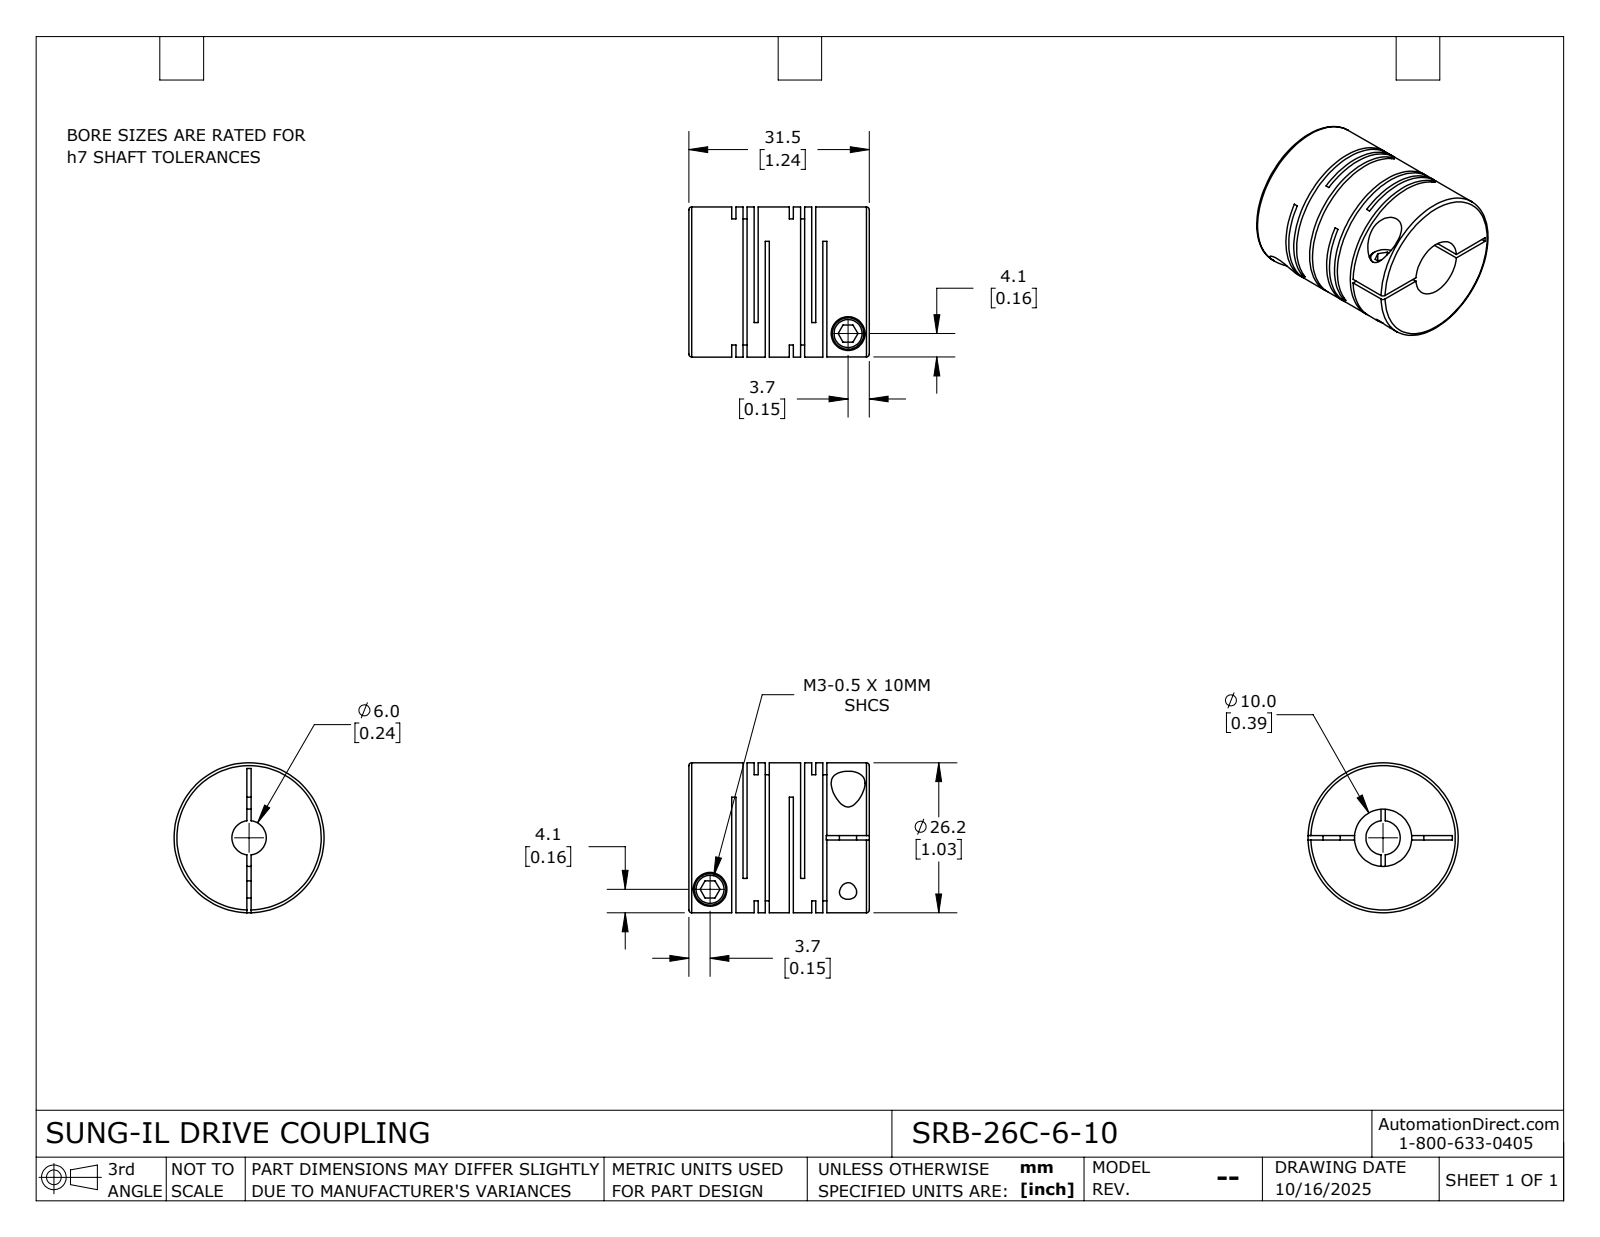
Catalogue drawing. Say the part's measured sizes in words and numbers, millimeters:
The part is named "SRB-26C-6-10". Its 3-D file was written by "SolidWorks 2024 (CONFIG_CONTROL_DESIGN)". It is 1 solid with 115 faces: 60 planar, 42 cylindrical and 13 other. Overall it measures 31.5 by 26.2 by 26.2 millimeters. Its volume is 12 296 cubic millimeters and its surface area 10 784 square millimeters. Round holes: 2 of diameter 3, 2 of diameter 5.9, 1 of diameter 6, 1 of diameter 10. Round bosses or shafts: 2 of diameter 5.5, 1 of diameter 26.2. The main face-to-face distances are 1.95, 10.05, 0.71, 3.9, 8.1, 12, 1.24, 2.66, 9.34, 13.95.
